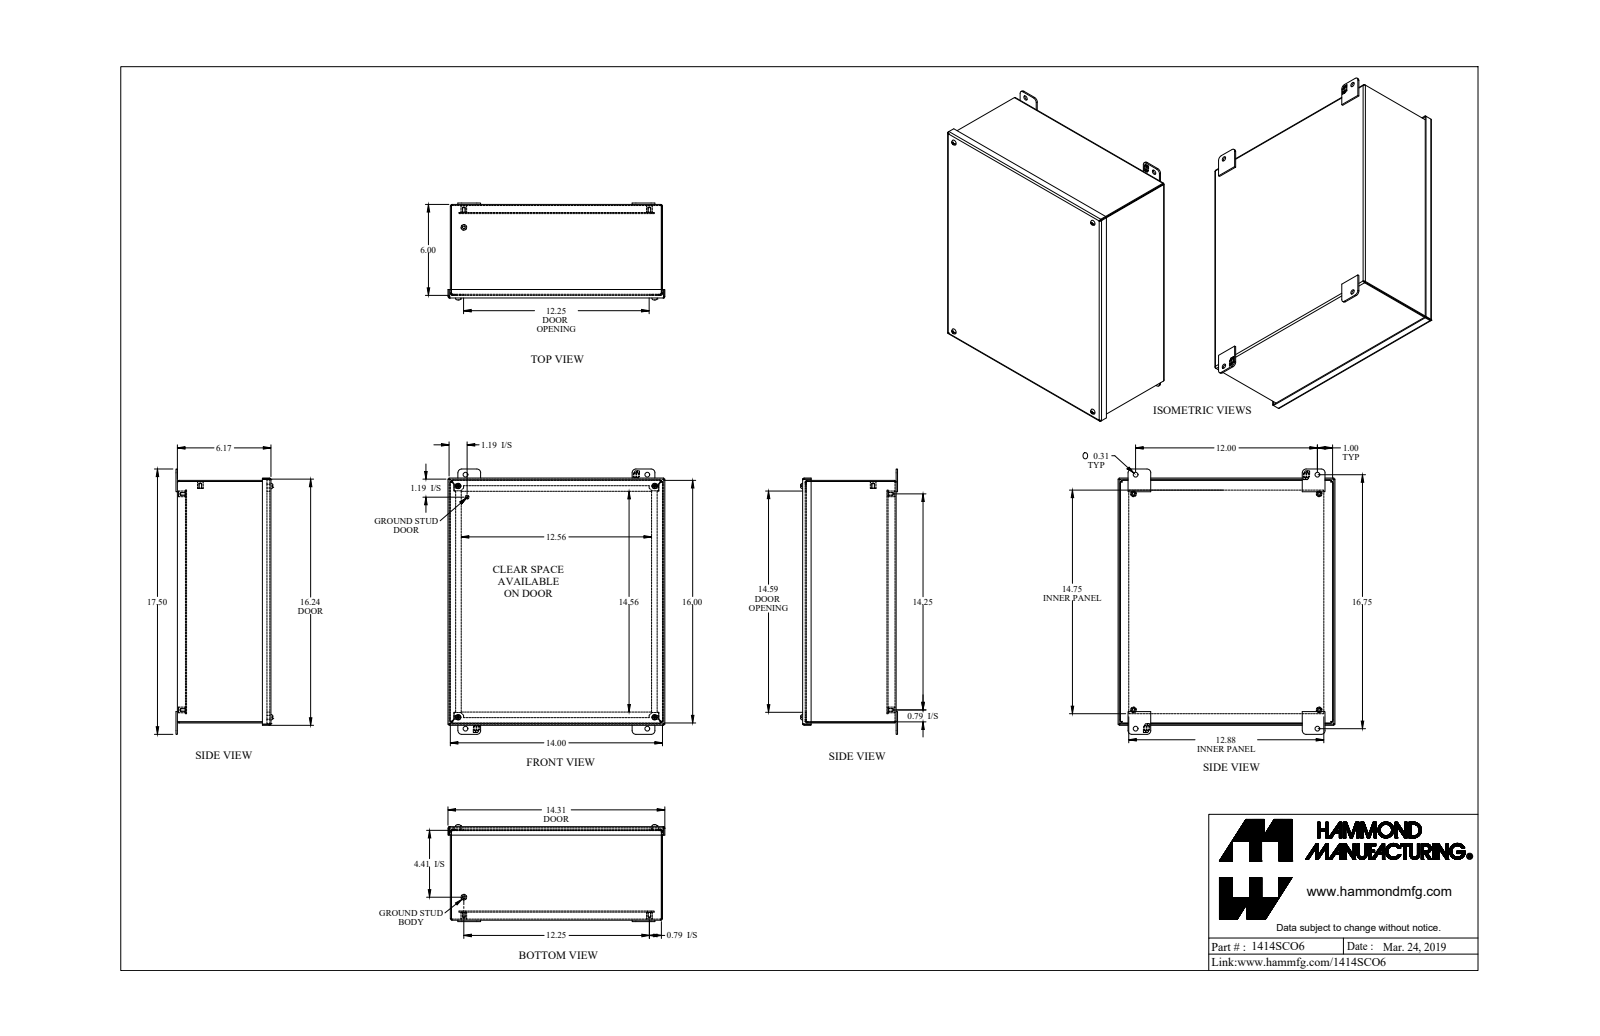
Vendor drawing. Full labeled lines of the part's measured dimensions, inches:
Part name (STEP PRODUCT): 1414SCO6
STEP written by: SolidWorks 2019 (AUTOMOTIVE_DESIGN)
Units: inches
Bodies: 30 solids, 662 faces (454 planar, 148 cylindrical, 60 other)
Overall size (bounding box): 17.5 × 14.312 × 6.394
Volume: 84.21 in³ · Surface area: 2 240 in²
Round holes (diameter × count): ⌀0.156 ×5, ⌀0.159 ×4, ⌀0.25 ×4, ⌀0.265 ×4, ⌀0.312 ×4
Round bosses / shafts (diameter × count): ⌀0.375 ×5, ⌀0.39 ×4, ⌀0.275 ×4, ⌀0.19 ×4, ⌀0.148 ×4, ⌀0.25 ×1, ⌀0.188 ×1
Partial cylindrical surfaces — rounded edges, fillets, slot ends (radius × count): R0.25 ×12, R0.007 ×8, R0.036 ×8, R0.079 ×8, R0.108 ×8, R0.125 ×8, R0.281 ×8, R0.16 ×4
Main face-to-face distances: 0.072, 6.1, 5.568, 0.532, 6.172, 6.028, 5.64, 0.46, 5.496, 0.604
Hole centre spacings: 12.502, 0.889, 16.008, 20.292, 12, 12.25, 12.956, 12.956
